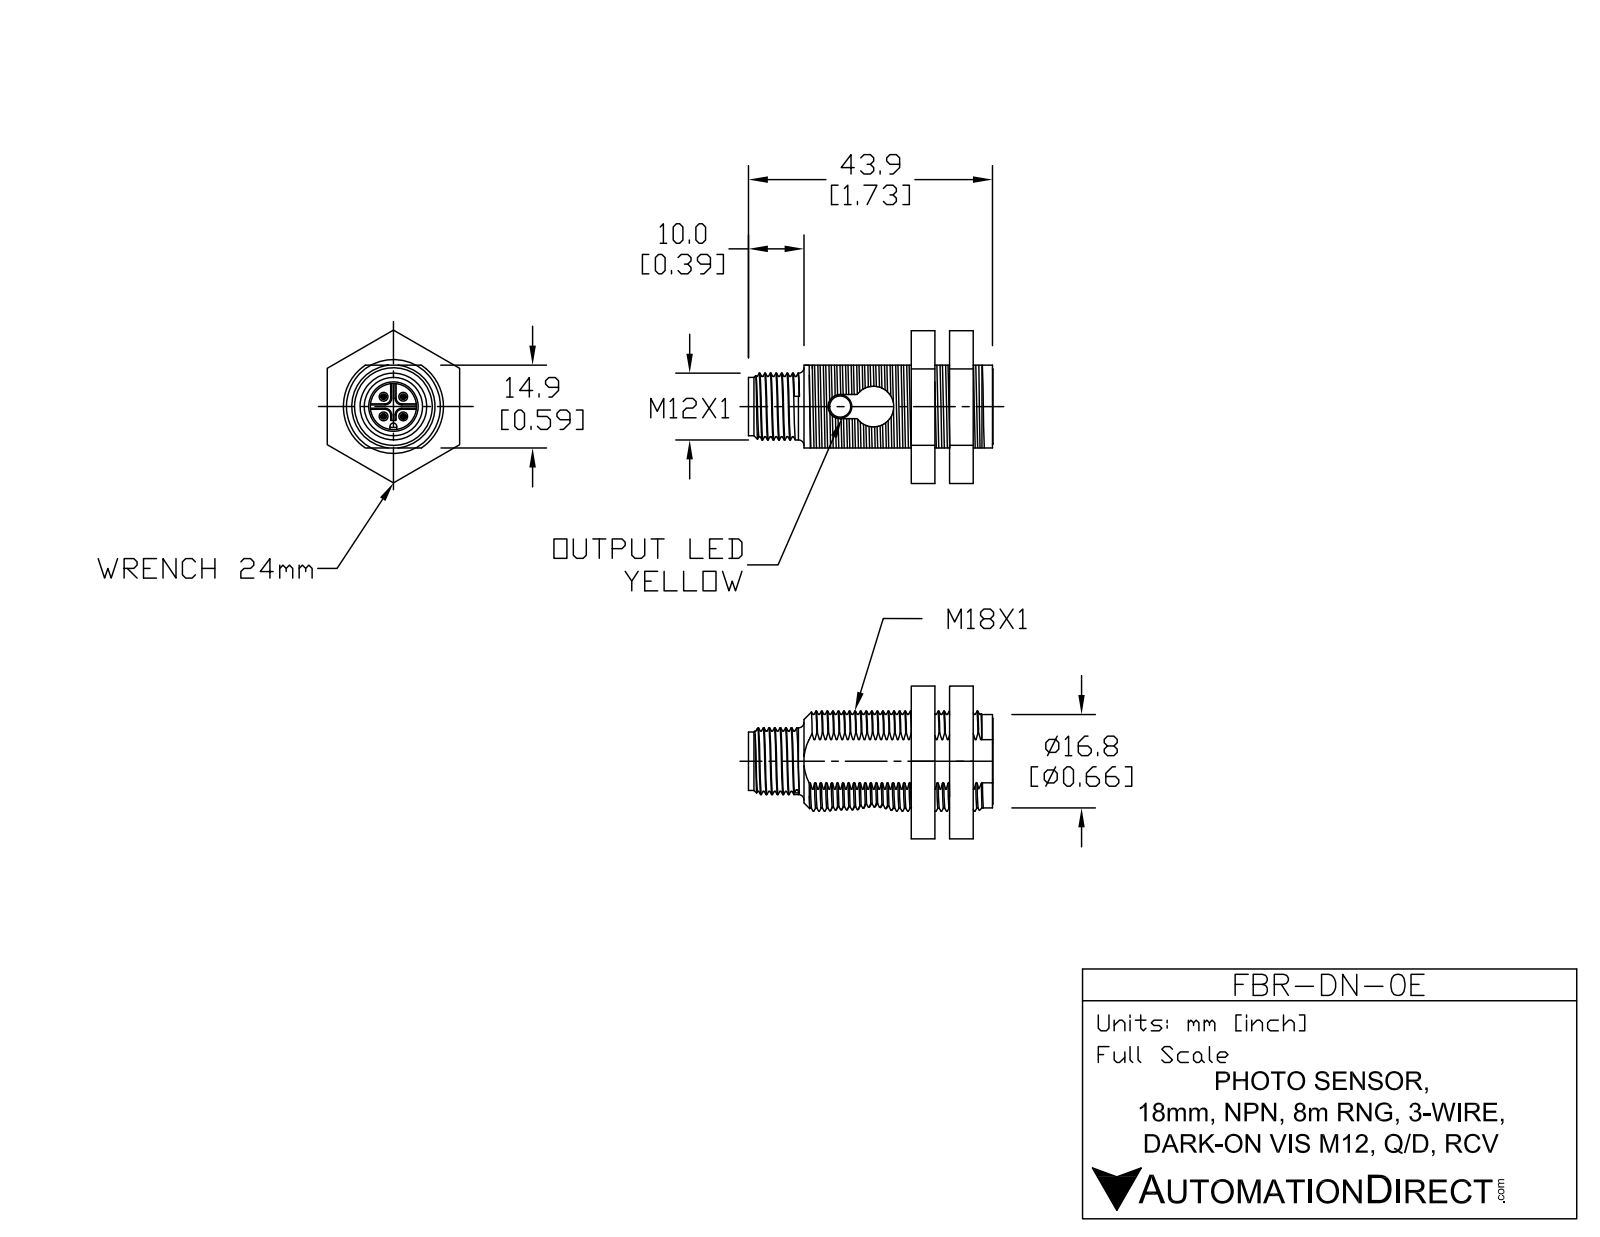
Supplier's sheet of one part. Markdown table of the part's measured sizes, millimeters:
| quantity | value |
| --- | --- |
| part name | FBR-DN-0E |
| STEP written by | SolidWorks 2011 (AUTOMOTIVE_DESIGN) |
| units | millimeters |
| bodies | 7 solids, 220 faces (132 planar, 30 cylindrical, 58 other) |
| overall size | 43.9 × 27.69 × 24.57 |
| volume | 10 286 mm³ |
| surface area | 5 155 mm² |
| round holes (diameter × count) | 2.36 × 1, 4.26 × 1, 7.25 × 1, 8.4 × 1 |
| round bosses / shafts (diameter × count) | 1 × 4, 12 × 1, 10.4 × 1 |
| partial cylindrical surfaces (radius × count) | 6.46 × 2, 7.46 × 2, 0.5 × 1, 8.4 × 1, 8.5 × 1, 9 × 1 |
| main face-to-face distances | 8, 4.5, 24, 15, 1, 12.5, 5.9, 13.9, 10.4, 18.4 |
| hole center spacings | 6.61 |
